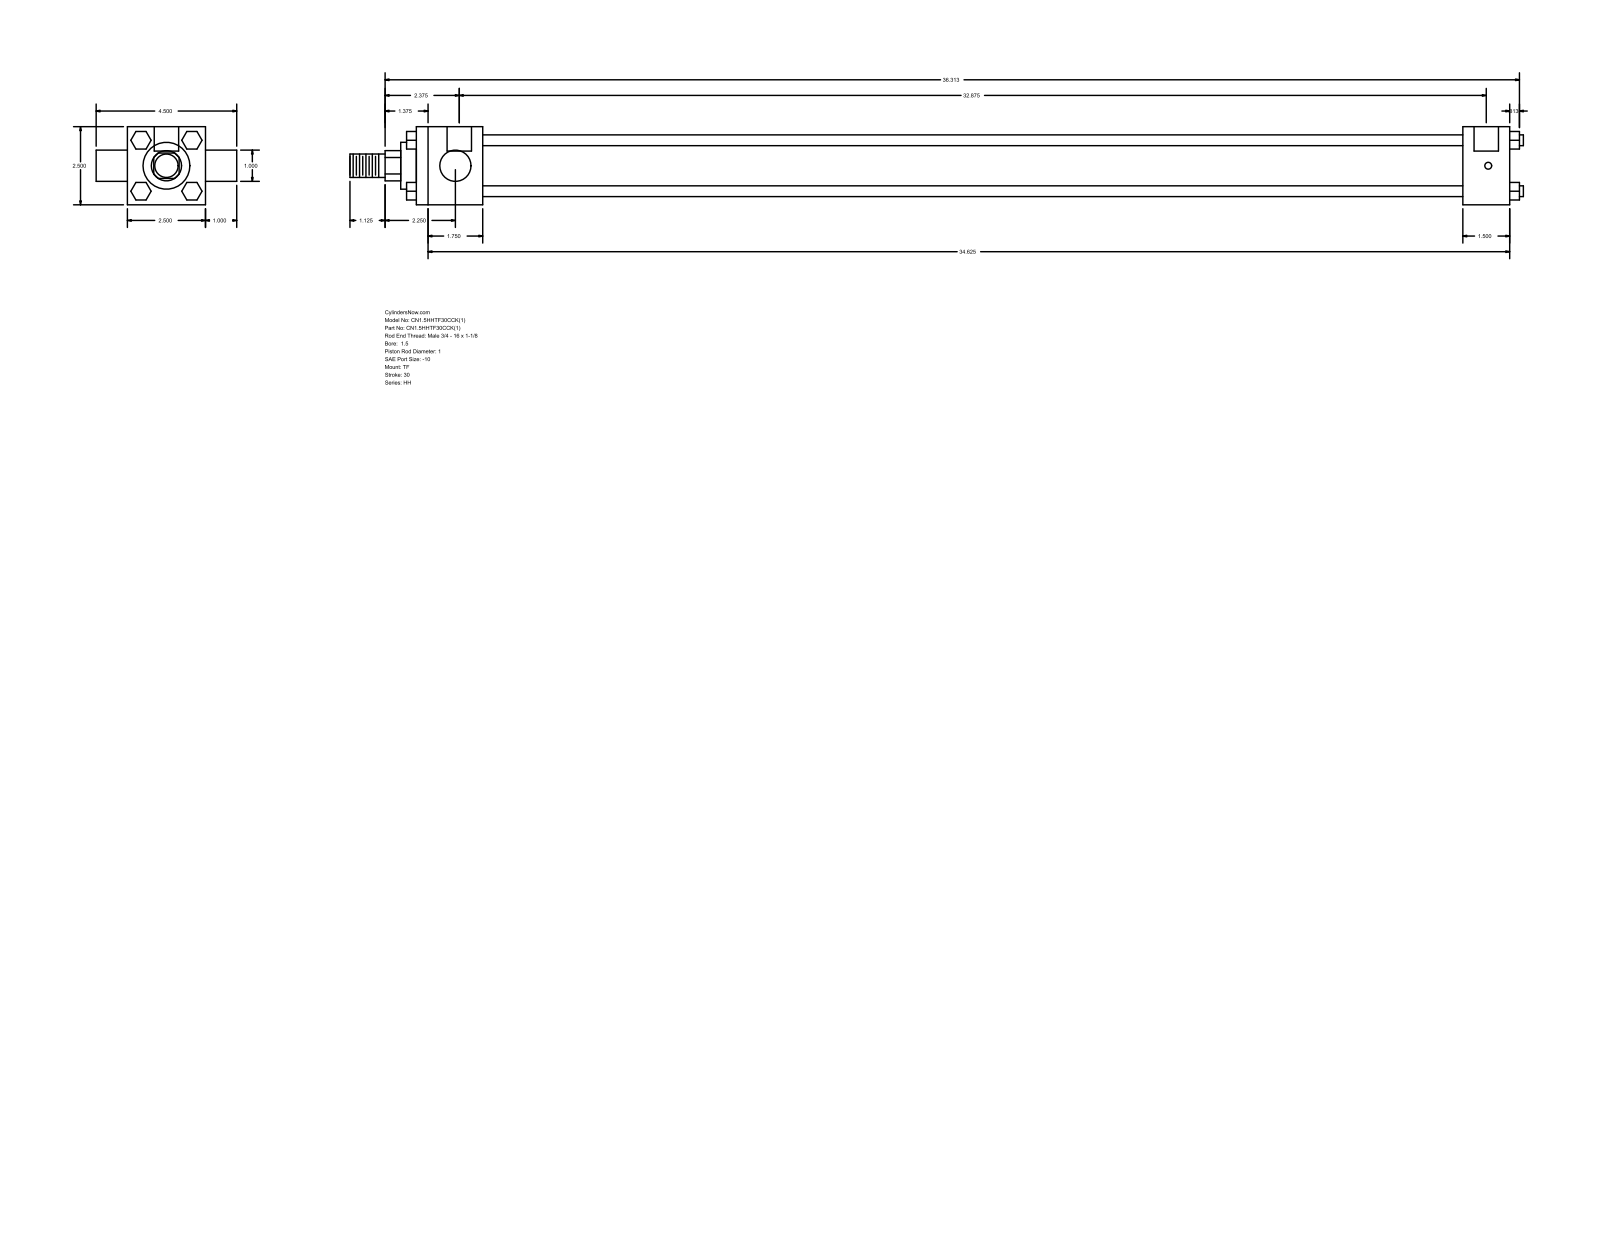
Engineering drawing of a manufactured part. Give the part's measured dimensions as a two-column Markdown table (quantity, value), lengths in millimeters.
| quantity | value |
| --- | --- |
| part name | HH_TF__0150_1 |
| STEP written by | GSSL Pune (CONFIG_CONTROL_DESIGN) |
| units | millimeters |
| bodies | 0 solids, 120 faces (92 planar, 28 cylindrical, 0 other) |
| overall size | 954.09 × 114.3 × 63.5 |
| round holes (diameter × count) | 5.56 × 3, 19.84 × 2 |
| round bosses / shafts (diameter × count) | 8.76 × 4, 25.4 × 2, 44.45 × 1, 38.1 × 1, 19.05 × 1 |
| partial cylindrical surfaces (radius × count) | 12.29 × 1 |
| main face-to-face distances | 63.5, 38.1, 835.02, 796.92, 53.98, 850.9, 889, 25.4, 20.7, 14.29 |
| hole center spacings | 1.59, 836.61, 835.02, 838.2 |
